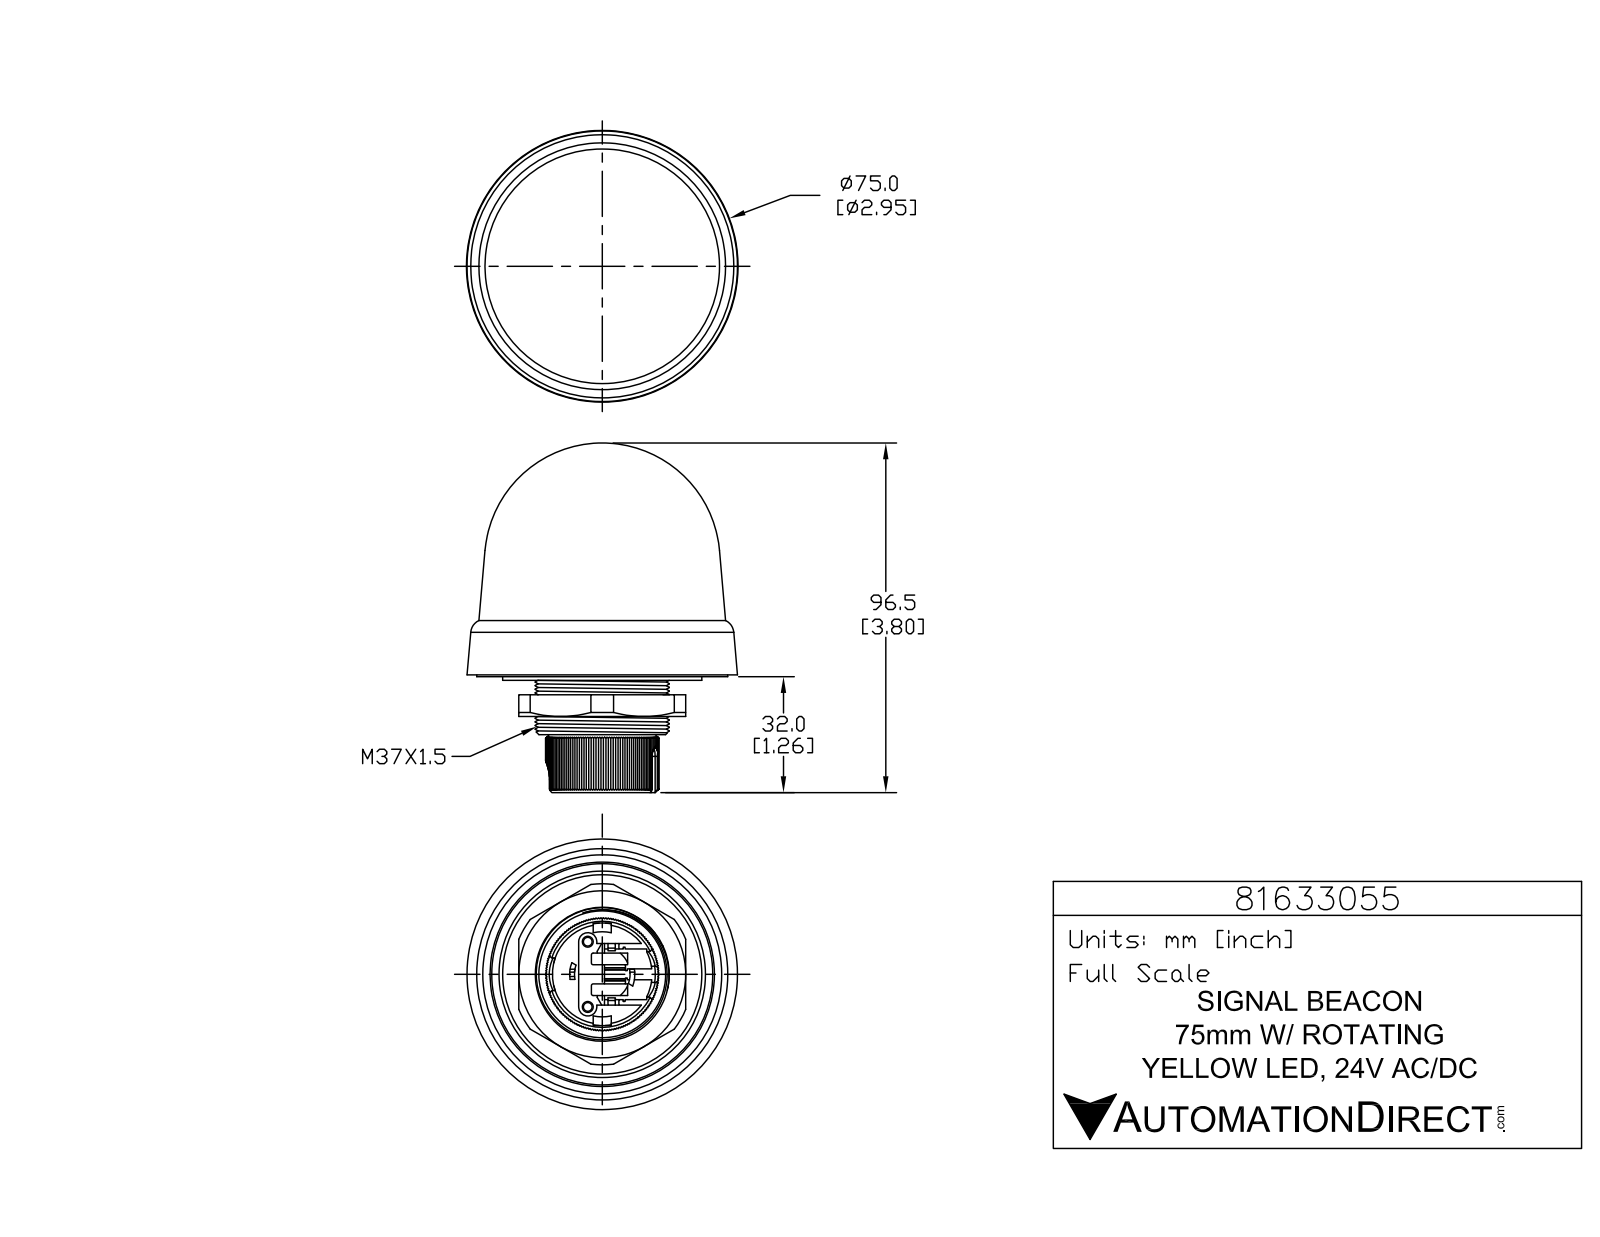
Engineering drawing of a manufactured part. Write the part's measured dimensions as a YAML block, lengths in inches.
part_name: "81633055"
step_written_by: "SolidWorks 2019 (CONFIG_CONTROL_DESIGN)"
units: inches
bodies: {solids: 3, faces: 560, planar: 432, cylindrical: 80, other: 48}
overall_size: [3.799, 2.941, 2.941]
volume: 12.36
surface_area: 58.68
round_holes:
  - {diameter: 0.094, count: 2}
  - {diameter: 0.118, count: 2}
  - {diameter: 0.604, count: 1}
  - {diameter: 1.142, count: 1}
round_bosses_or_shafts:
  - {diameter: 0.217, count: 2}
  - {diameter: 0.067, count: 2}
  - {diameter: 2.165, count: 1}
  - {diameter: 1.457, count: 1}
  - {diameter: 0.925, count: 1}
partial_cylinders:
  - {radius: 0.008, count: 6}
  - {radius: 0.039, count: 6}
  - {radius: 0.02, count: 4}
  - {radius: 0.031, count: 2}
  - {radius: 0.079, count: 2}
  - {radius: 0.098, count: 2}
  - {radius: 0.177, count: 1}
  - {radius: 0.354, count: 1}
face_to_face_distances: [0.177, 0.354, 0.197, 0.433, 0.512, 0.335, 0.059, 0.394, 0.118, 0.157]
hole_center_spacings: [0.388, 0.709]
